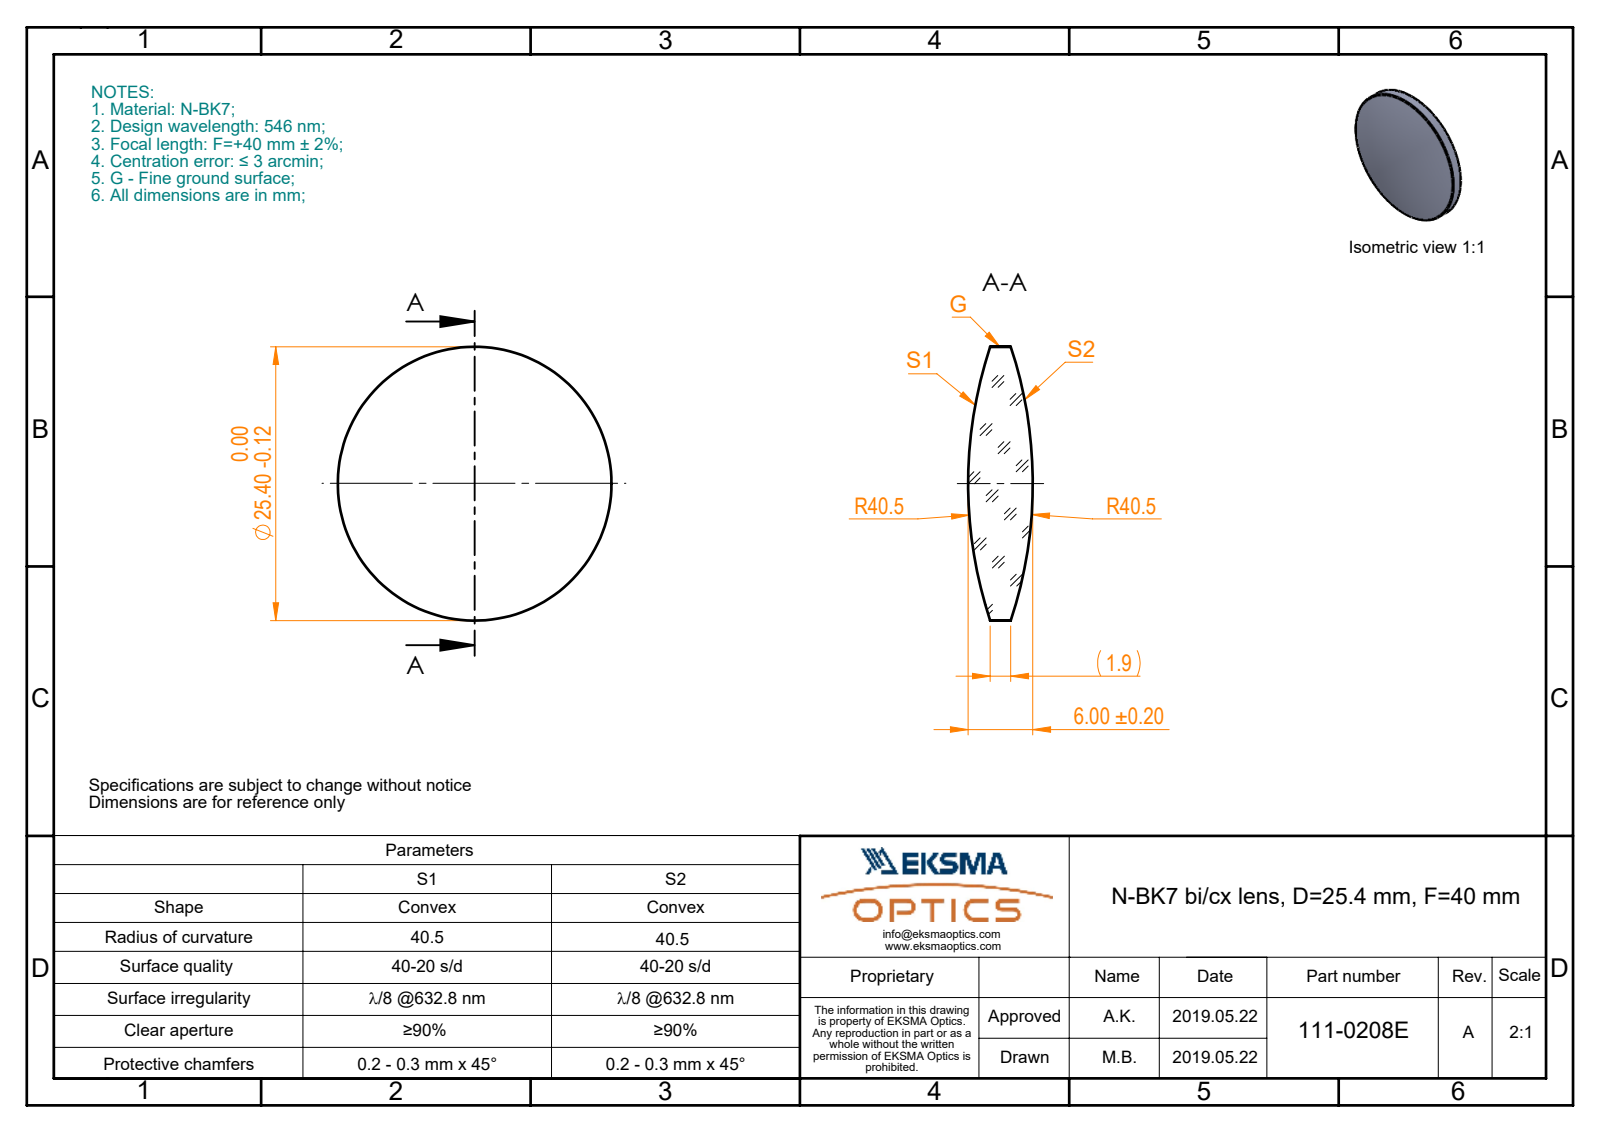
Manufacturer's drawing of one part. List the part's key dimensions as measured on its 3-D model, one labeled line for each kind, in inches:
Part name (STEP PRODUCT): 111-0208E BK7 bi-cx 25.4 F40
STEP written by: SolidWorks 2017 (CONFIG_CONTROL_DESIGN)
Units: inches
Bodies: 1 solid, 6 faces (0 planar, 2 cylindrical, 4 other)
Overall size (bounding box): 1 × 1 × 0.236
Volume: 0.123 in³ · Surface area: 1.848 in²
Round bosses / shafts (diameter × count): ⌀1 ×1
